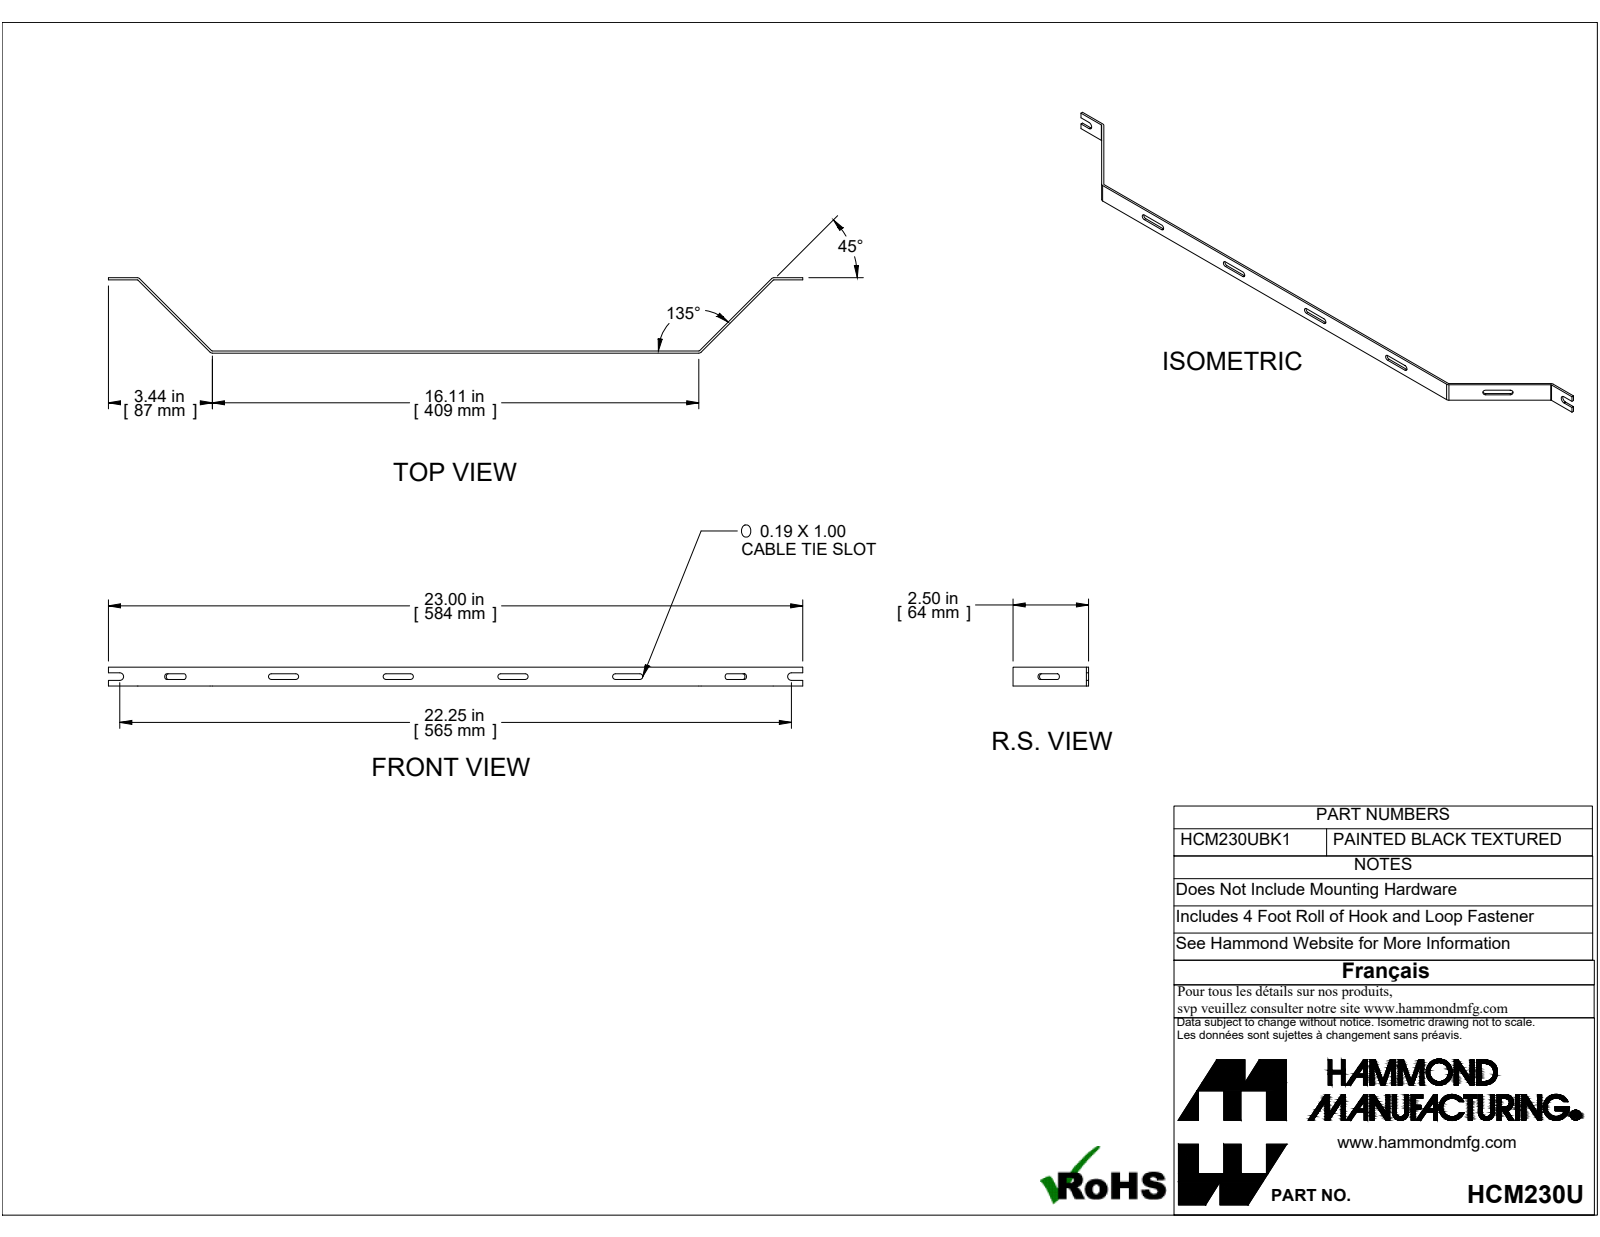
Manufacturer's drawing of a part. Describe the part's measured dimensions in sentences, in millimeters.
Its 3-D file was written by "Unknown (AUTOMOTIVE_DESIGN)". It is 1 solid with 54 faces: 32 planar, 22 cylindrical and 0 other. Overall it measures 584.2 by 63.5 by 15.88 millimeters. Its volume is 16 878 cubic millimeters and its surface area 21 539 square millimeters. Partial cylindrical surfaces (rounded edges, fillets, slot ends): 12 of radius 2.39, 4 of radius 0.91, 4 of radius 2.74, 2 of radius 3.17. The main face-to-face distances are 1.83, 61.67, 15.88, 63.5, 59.84, 5.55, 10.33, 4.78, 4.77, 11.11.
